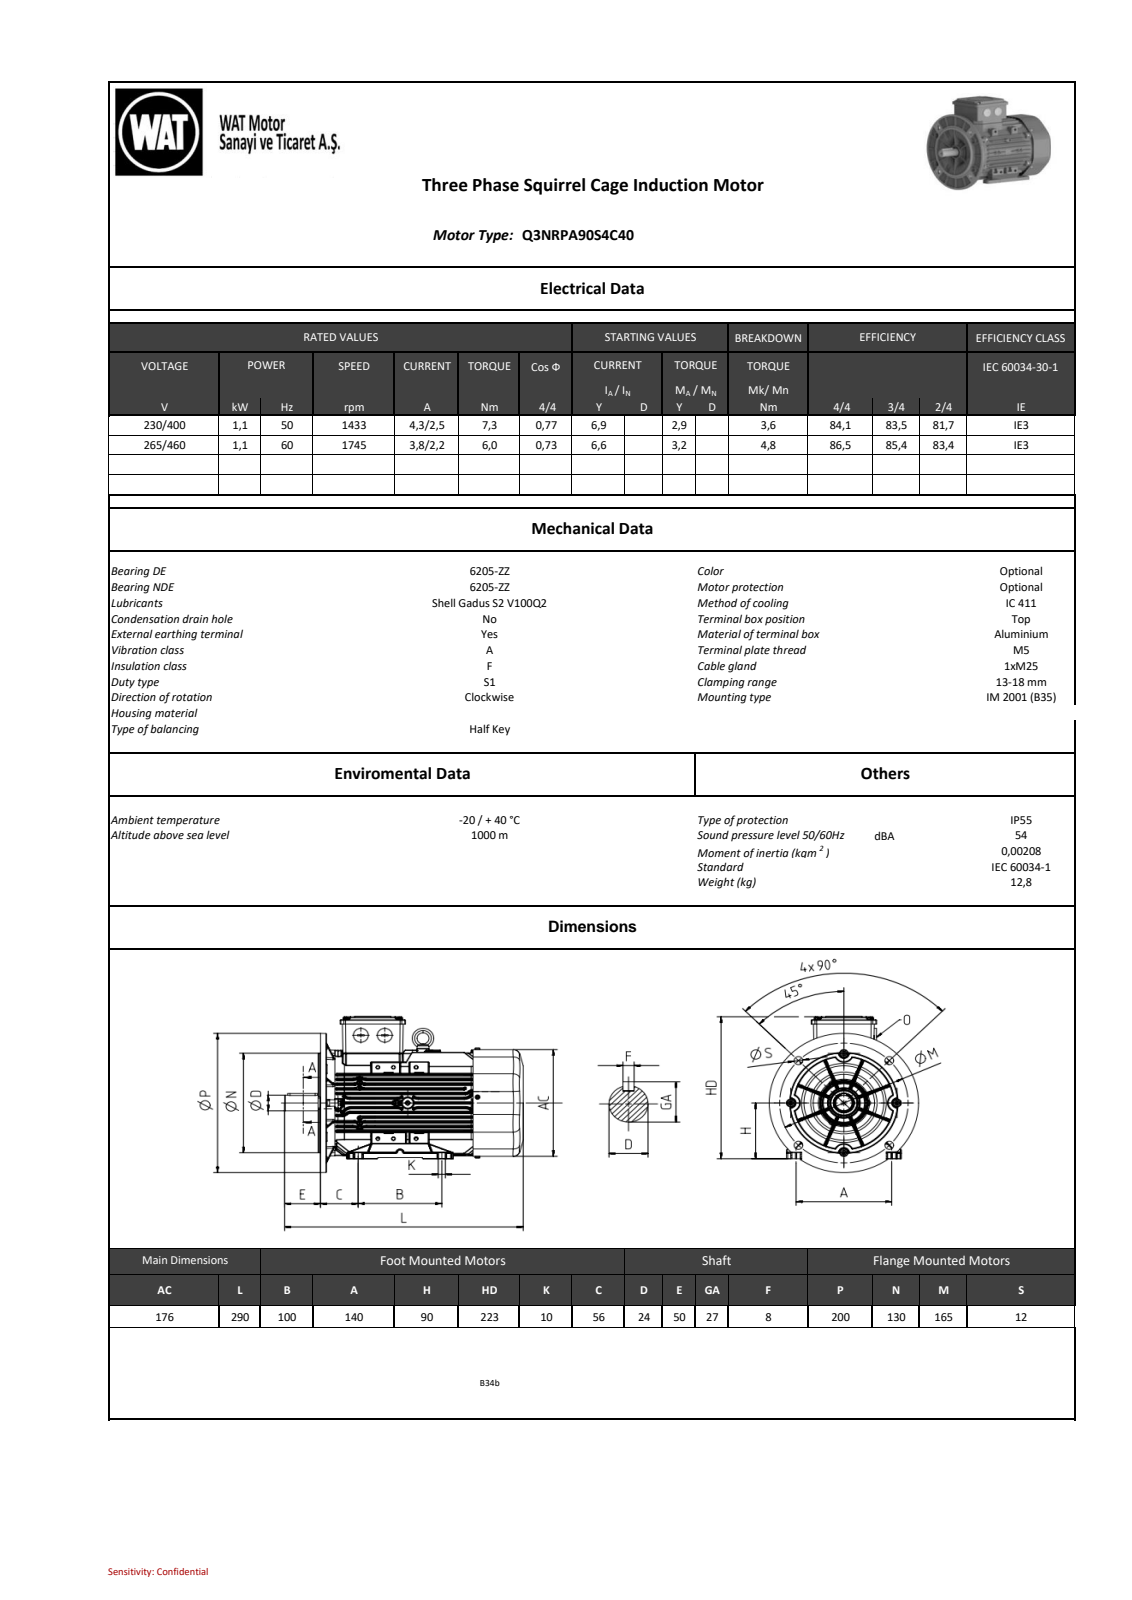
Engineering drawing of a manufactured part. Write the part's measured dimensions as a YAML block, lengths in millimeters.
part_name: "C9011714D8875qxt"
step_written_by: "SIEMENS PLM Software NX 11.0 (AUTOMOTIVE_DESIGN)"
units: millimeters
bodies: {solids: 0, faces: 15416, planar: 3626, cylindrical: 4793, other: 6997}
overall_size: [290, 219.47, 198.95]
round_holes:
  - {diameter: 4.2, count: 6}
  - {diameter: 9, count: 6}
  - {diameter: 5.1, count: 5}
  - {diameter: 12, count: 4}
  - {diameter: 2, count: 2}
  - {diameter: 2.5, count: 2}
  - {diameter: 3, count: 2}
  - {diameter: 7, count: 2}
  - {diameter: 4, count: 1}
  - {diameter: 8, count: 1}
  - {diameter: 12.2, count: 1}
  - {diameter: 23.9, count: 1}
round_bosses_or_shafts:
  - {diameter: 5, count: 12}
  - {diameter: 8, count: 8}
  - {diameter: 4, count: 8}
  - {diameter: 9.4, count: 6}
  - {diameter: 8.5, count: 6}
  - {diameter: 9.2, count: 5}
  - {diameter: 25, count: 3}
  - {diameter: 35, count: 2}
partial_cylinders:
  - {radius: 0.5, count: 1380}
  - {radius: 1, count: 668}
  - {radius: 0.8, count: 503}
  - {radius: 0.2, count: 144}
  - {radius: 0.3, count: 114}
  - {radius: 1.5, count: 110}
  - {radius: 2, count: 99}
  - {radius: 4, count: 88}
face_to_face_distances: [0.8, 5.51, 56, 6, 70, 2, 28, 39, 5.5, 145]
hole_center_spacings: [20, 81, 14.14, 14.15, 28.28, 92.93, 132.7, 14.39]
